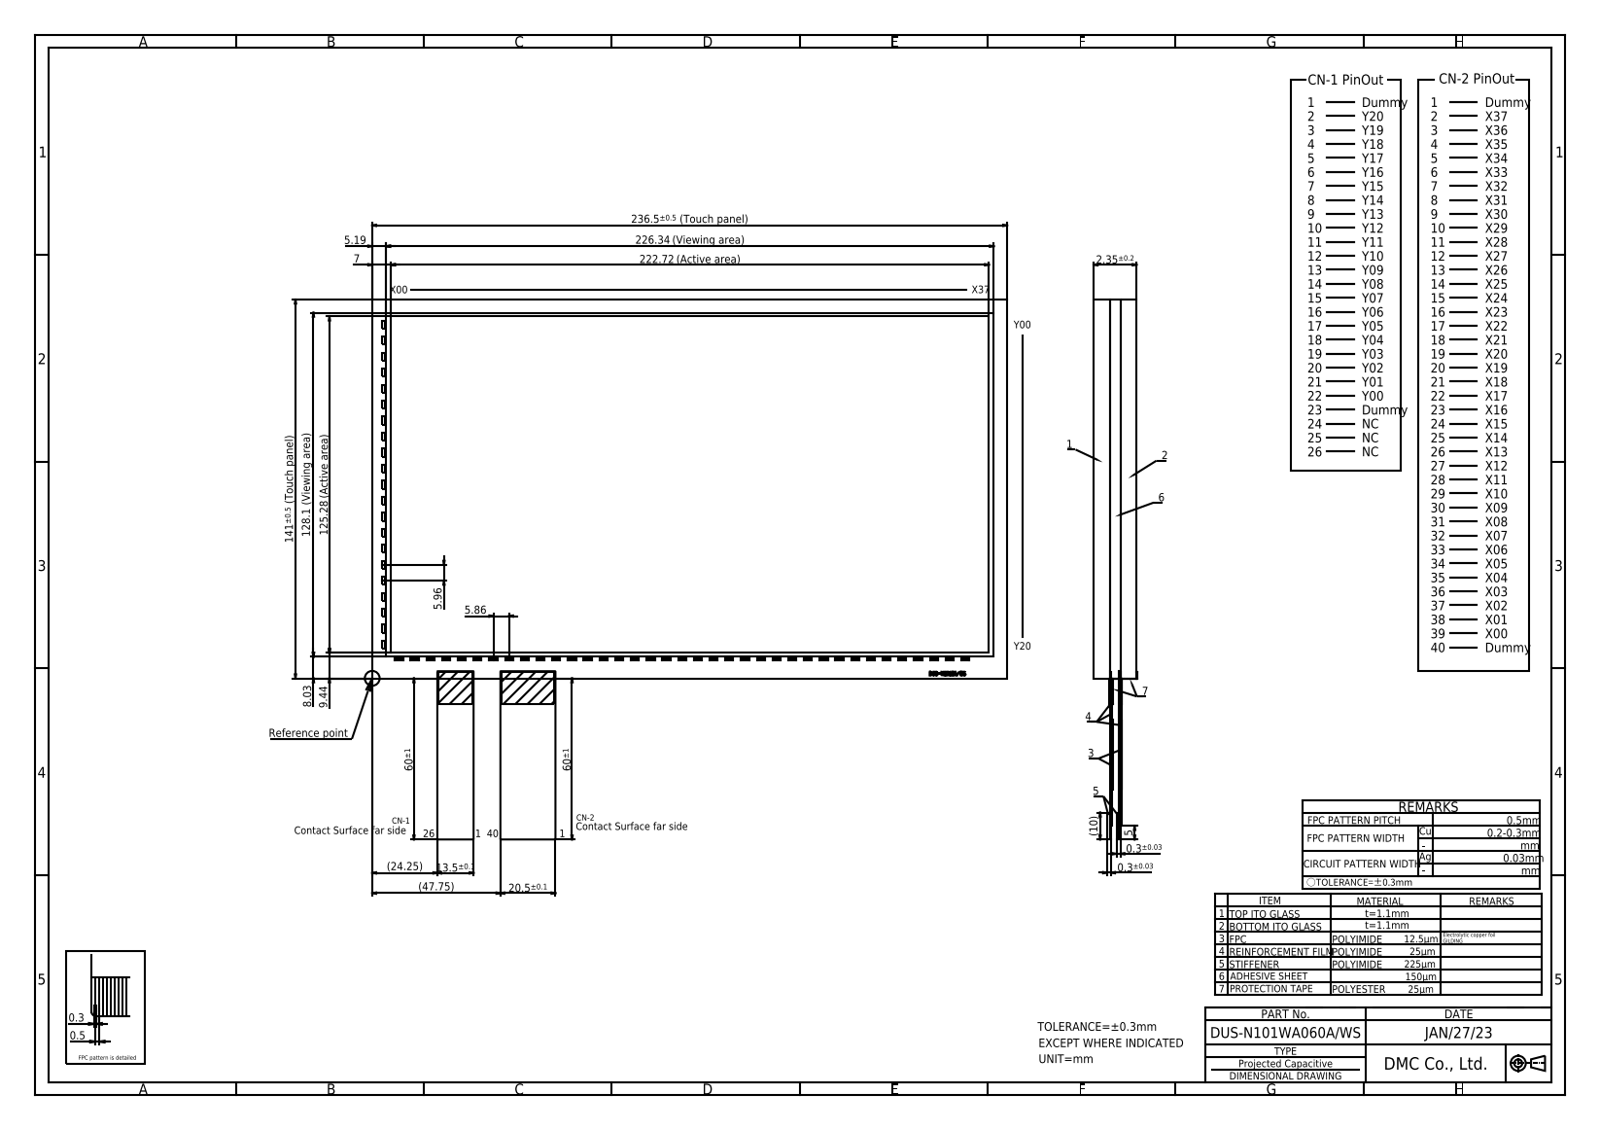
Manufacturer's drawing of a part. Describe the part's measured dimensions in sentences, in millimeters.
The part is named "DUS-N101WA060A_WS". Its 3-D file was written by "Autodesk Inventor 2020 (AUTOMOTIVE_DESIGN)". It is 1 solid with 292 faces: 288 planar, 4 cylindrical and 0 other. Overall it measures 331.1 by 229.2 by 2.35 millimeters. Its volume is 78 653 cubic millimeters and its surface area 72 608 square millimeters. Partial cylindrical surfaces (rounded edges, fillets, slot ends): 4 of radius 0.2. The main face-to-face distances are 2.35, 1.2, 1.15, 1.25, 1.1, 141, 0.8, 1.55, 0.4, 236.5.
